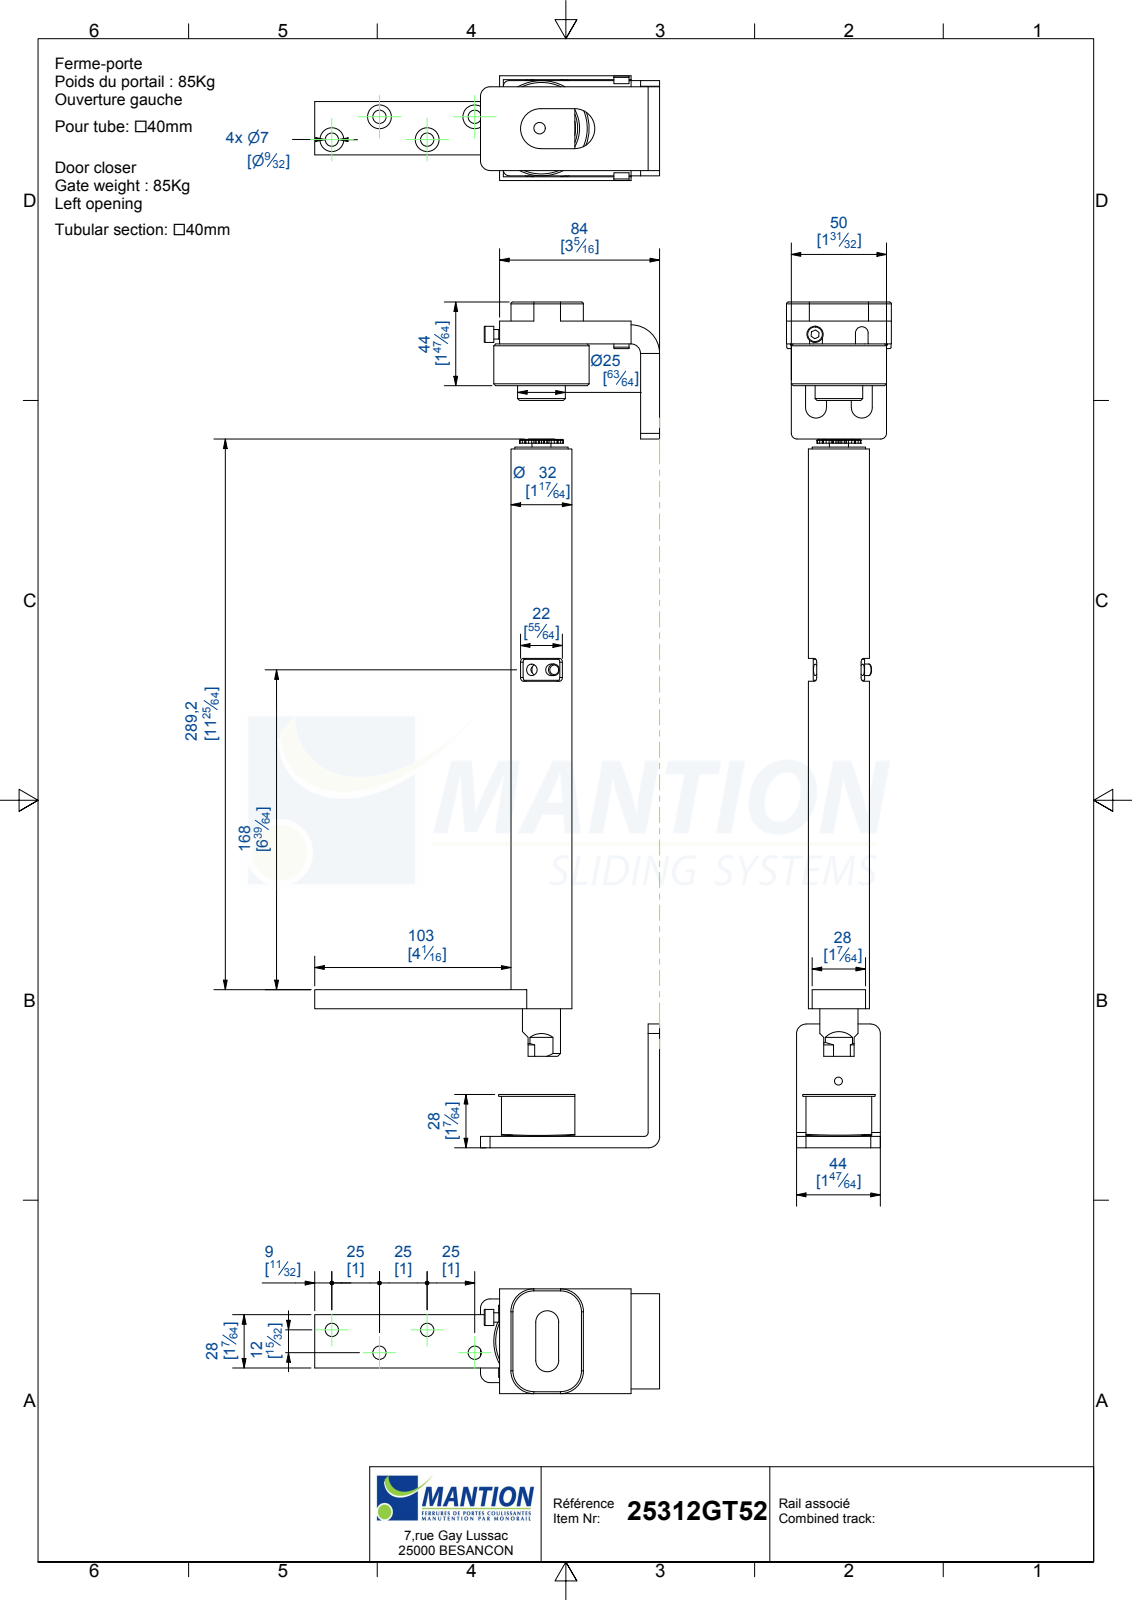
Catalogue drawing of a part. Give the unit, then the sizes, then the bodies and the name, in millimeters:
Units: millimetres
Overall size (bounding box): 444.2 × 181 × 55
Round holes (diameter × count): ⌀6 ×9, ⌀7 ×4, ⌀2.46 ×2, ⌀4.13 ×2, ⌀4.5 ×2, ⌀10.2 ×2, ⌀16 ×1, ⌀17 ×1, ⌀20 ×1, ⌀25 ×1, ⌀28 ×1, ⌀30 ×1
Round bosses / shafts (diameter × count): ⌀10 ×3, ⌀18 ×2, ⌀14.63 ×2, ⌀50 ×1, ⌀32 ×1, ⌀27 ×1, ⌀24.9 ×1, ⌀16.9 ×1
Partial cylindrical surfaces — rounded edges, fillets, slot ends (radius × count): R1 ×52, R0.5 ×24, R2 ×9, R5.5 ×8, R5 ×5, R3 ×4, R10 ×4, R12 ×4
Main face-to-face distances: 10, 6, 2, 83, 11, 77, 73, 22, 349.2, 12
Hole centre spacings: 27.73, 12, 12.04, 12.26, 19.3, 20.41, 35.51, 50
Volume: 274 094 mm³ · Surface area: 137 243 mm²
Bodies: 14 solids, 661 faces (319 planar, 202 cylindrical, 140 other)
Part name (STEP PRODUCT): 25312GT52
STEP written by: Autodesk Inventor 2019 (AUTOMOTIVE_DESIGN)
